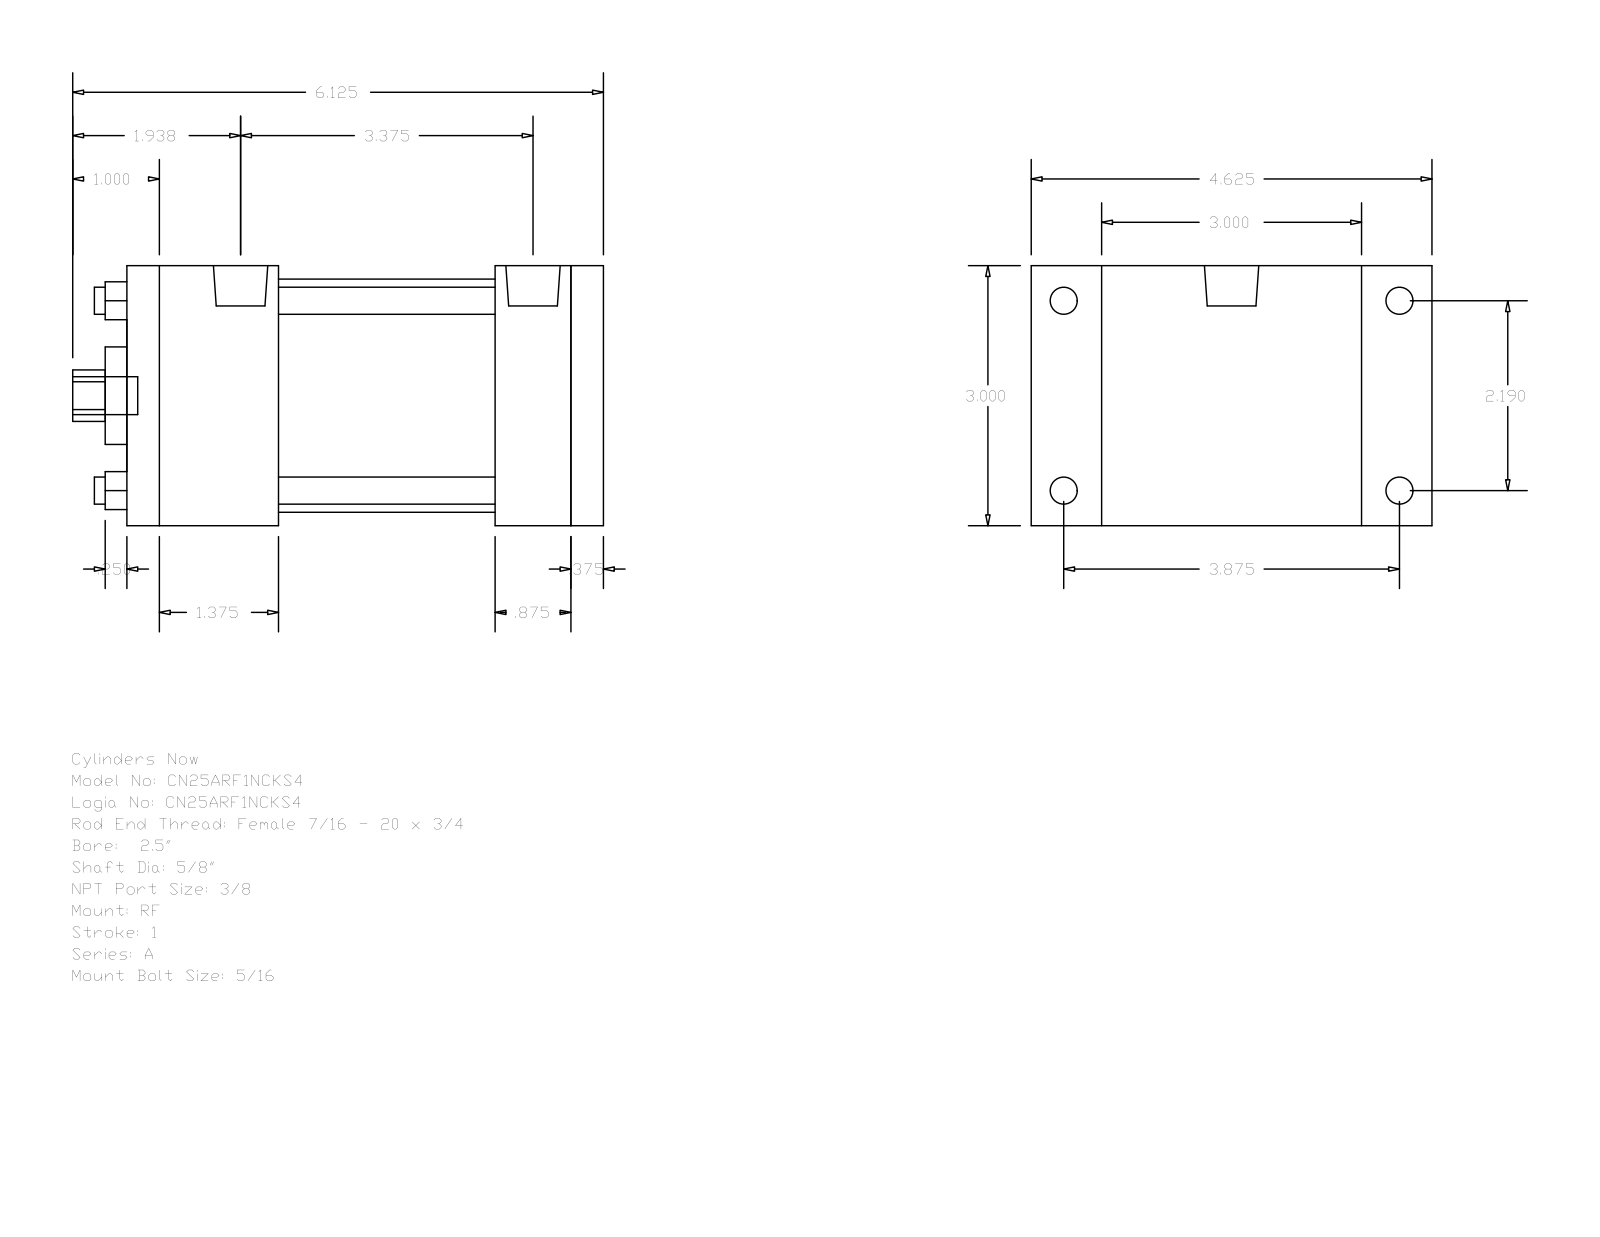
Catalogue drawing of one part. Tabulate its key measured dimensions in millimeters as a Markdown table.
| quantity | value |
| --- | --- |
| part name | A_RF__0250_0.625 |
| STEP written by | GSSL Pune (CONFIG_CONTROL_DESIGN) |
| units | millimeters |
| bodies | 0 solids, 92 faces (64 planar, 28 cylindrical, 0 other) |
| overall size | 155.57 × 117.47 × 76.2 |
| round holes (diameter × count) | 7.94 × 4, 15.88 × 1, 28.57 × 1, 68.33 × 1 |
| round bosses / shafts (diameter × count) | 7.94 × 4, 5.56 × 4, 15.93 × 2, 11.11 × 1 |
| partial cylindrical surfaces (radius × count) | 7.54 × 1 |
| main face-to-face distances | 76.2, 139.69, 9.52, 130.17, 44.45, 107.95, 63.5, 85.72, 95.24, 22.22 |
| hole center spacings | 39.33, 55.62, 78.66 |
